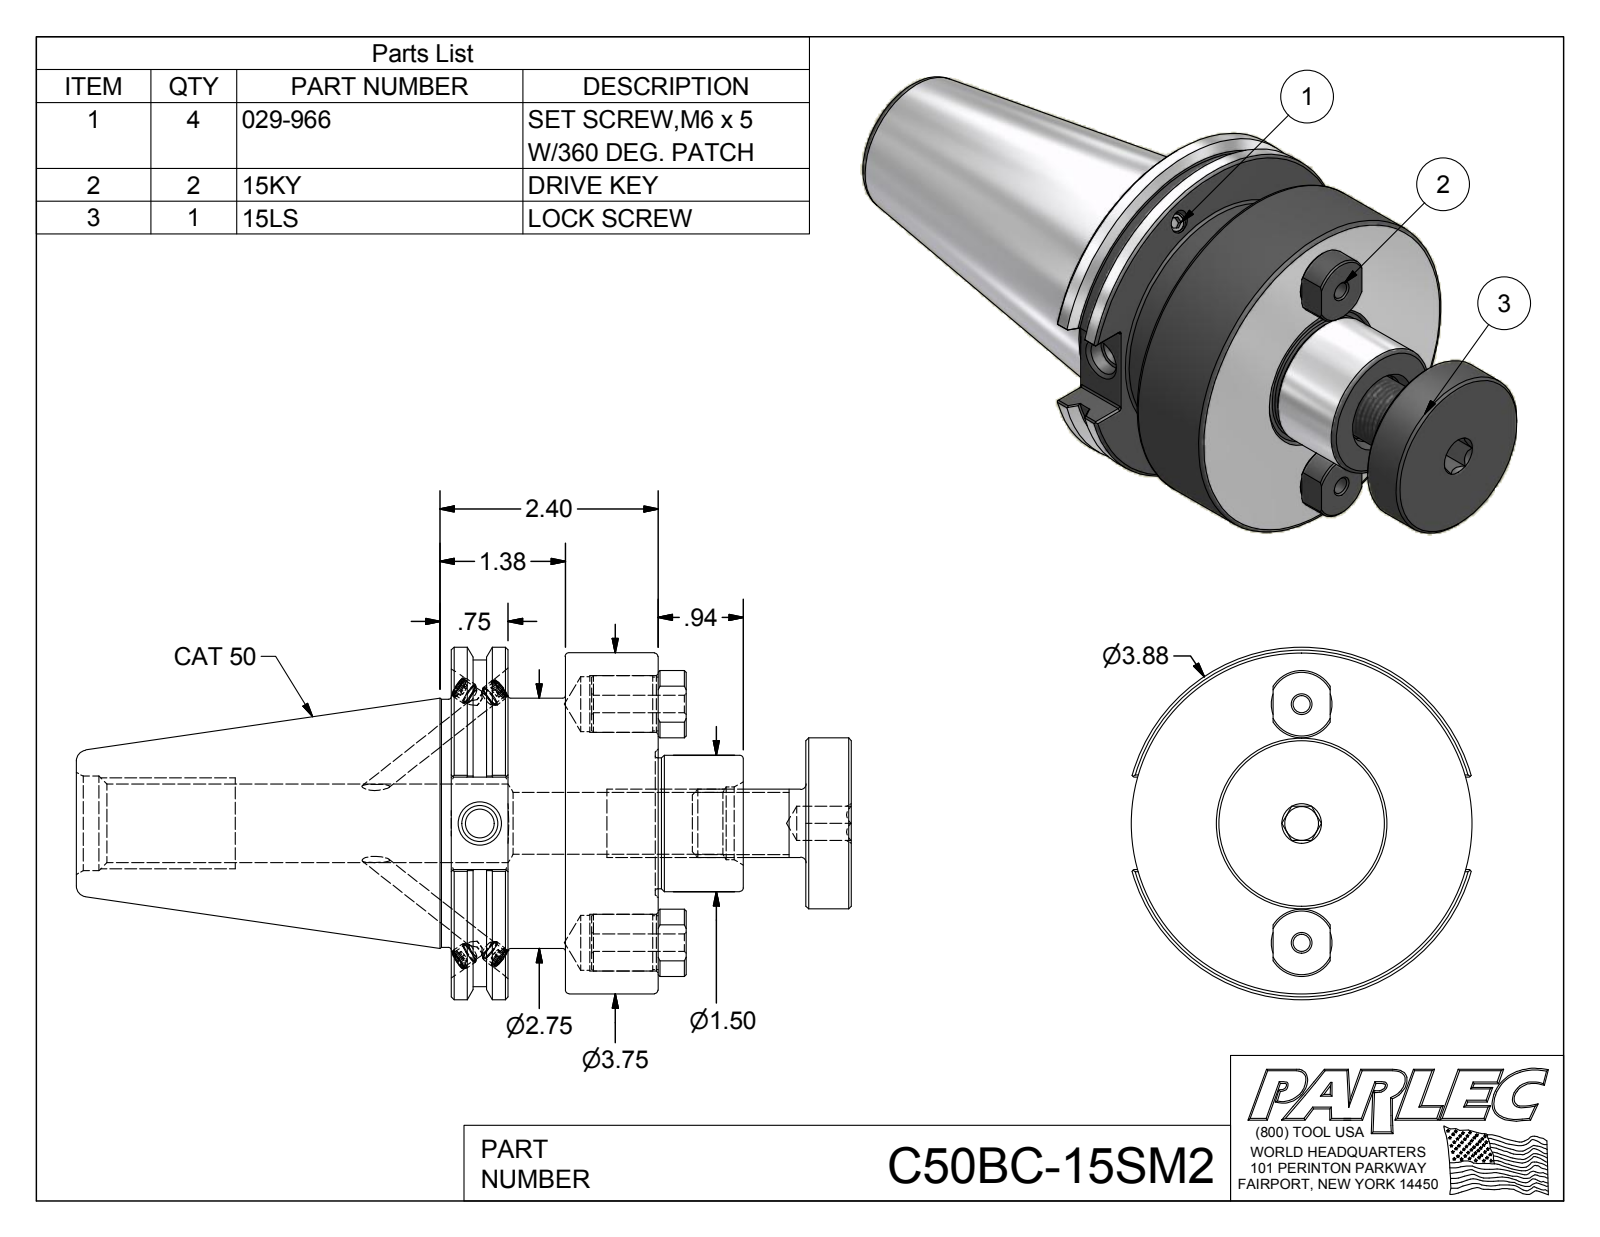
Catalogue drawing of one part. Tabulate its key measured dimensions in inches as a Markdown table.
| quantity | value |
| --- | --- |
| part name | C50BC-15SM2; C50BC-15SM2-1; 15KY; 15LS (+1 more) |
| STEP written by | Autodesk Inventor 2012 (AUTOMOTIVE_DESIGN) |
| units | inches |
| bodies | 8 solids, 248 faces (107 planar, 66 cylindrical, 75 other) |
| overall size | 8.525 × 3.875 × 3.75 |
| volume | 36.84 in³ |
| surface area | 131.3 in² |
| round holes (diameter × count) | 0.197 × 4, 0.24 × 4, 0.19 × 2, 0.604 × 2, 0.624 × 2, 0.315 × 1, 0.375 × 1, 0.399 × 1, 0.682 × 1, 0.8 × 1, 0.865 × 1, 1.038 × 1 |
| round bosses / shafts (diameter × count) | 0.244 × 4, 0.236 × 4, 0.626 × 2, 0.59 × 2, 3.875 × 1, 3.75 × 1, 3.594 × 1, 2.75 × 1 |
| partial cylindrical surfaces (radius × count) | 0.02 × 12, 0.37 × 2 |
| main face-to-face distances | 1.02, 1.255, 2.275, 0.625, 0.63, 1.65, 4.4, 3.775, 3.145, 2.125 |
| hole center spacings | 1.312, 2.624 |
